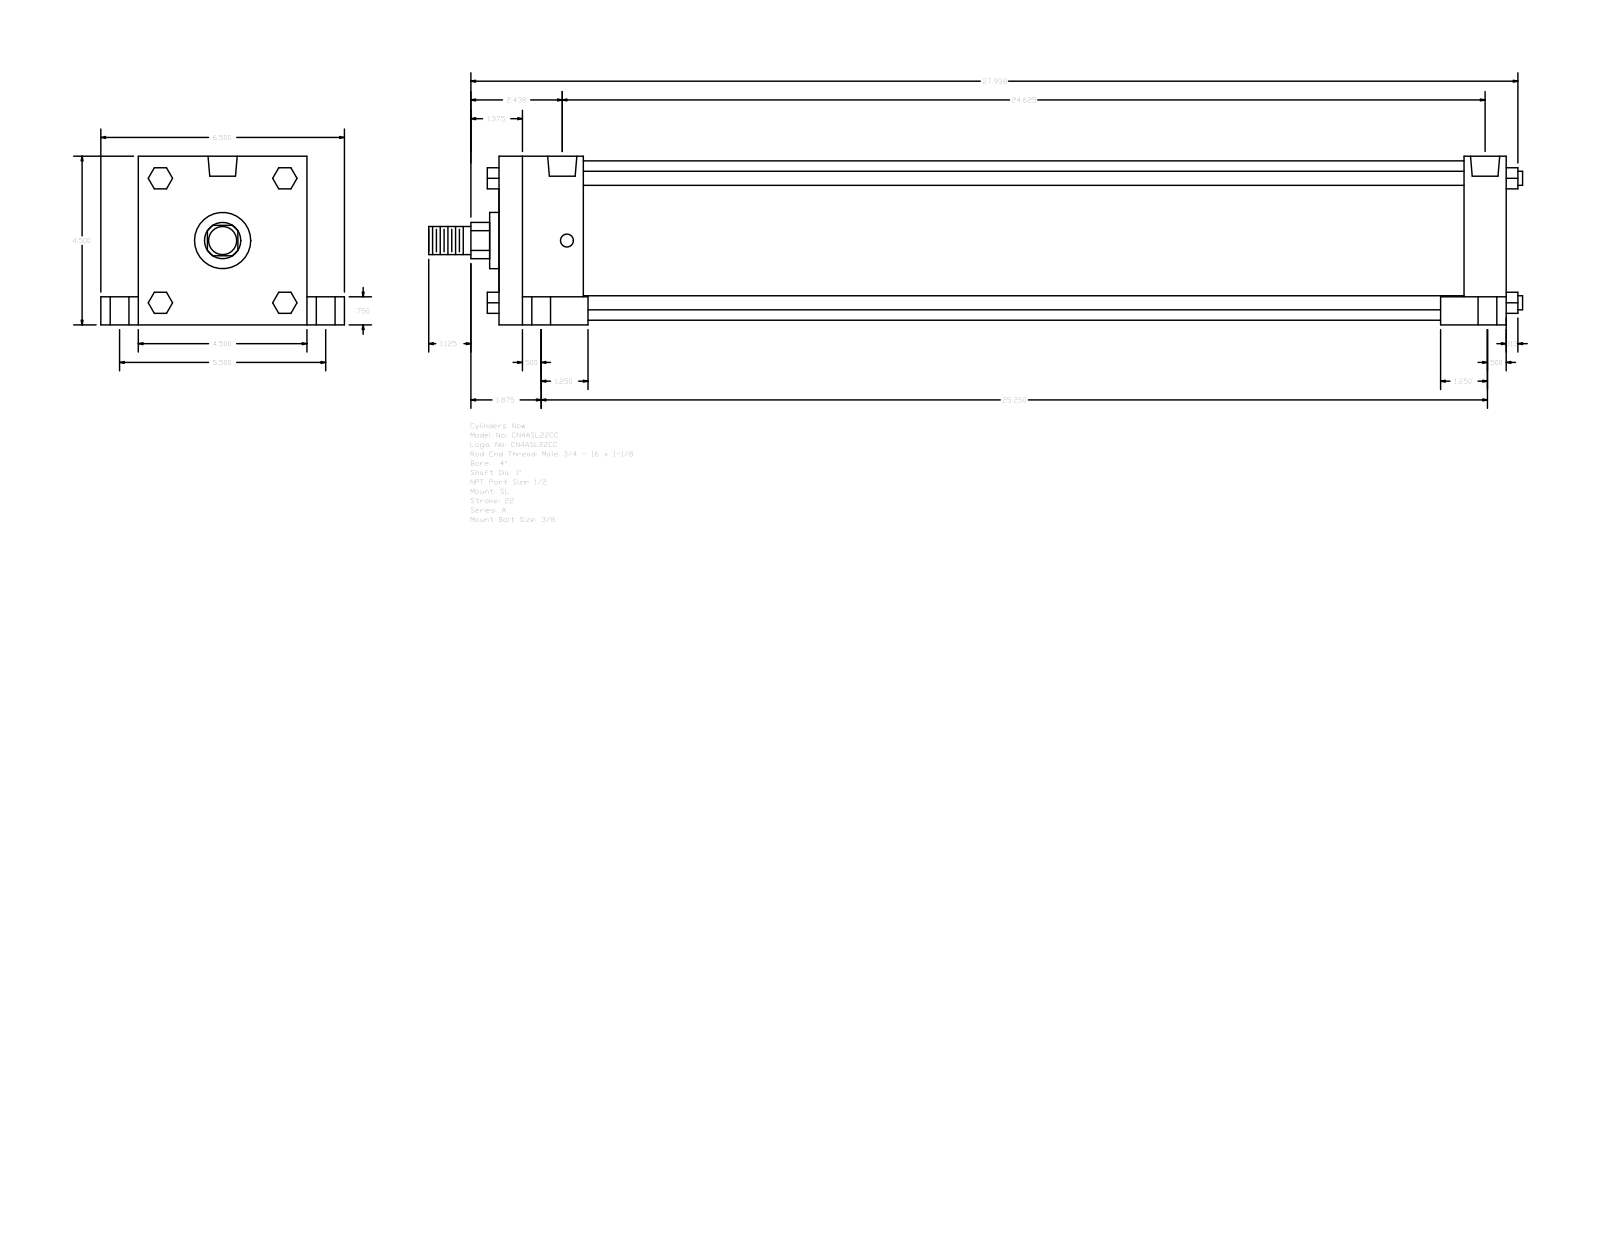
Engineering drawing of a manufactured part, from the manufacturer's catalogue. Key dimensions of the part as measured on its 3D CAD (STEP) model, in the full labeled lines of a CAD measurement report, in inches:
Part name (STEP PRODUCT): A_SL__0400_1
STEP written by: GSSL Pune (CONFIG_CONTROL_DESIGN)
Units: inches
Bodies: 0 solids, 150 faces (114 planar, 36 cylindrical, 0 other)
Overall size (bounding box): 29.187 × 6.5 × 4.5
Round holes (diameter × count): ⌀0.344 ×4, ⌀0.5 ×4, ⌀0.75 ×4, ⌀0.778 ×2
Round bosses / shafts (diameter × count): ⌀0.375 ×4, ⌀4.25 ×1, ⌀1.5 ×1, ⌀1 ×1, ⌀0.75 ×1
Partial cylindrical surfaces — rounded edges, fillets, slot ends (radius × count): R0.484 ×1
Main face-to-face distances: 4.5, 26.875, 1.125, 2.25, 24.625, 25.75, 23.5, 0.75, 1, 5.5
Hole centre spacings: 0.125, 2.751, 2.756, 2.807, 2.835, 5.5, 24.375, 24.5
